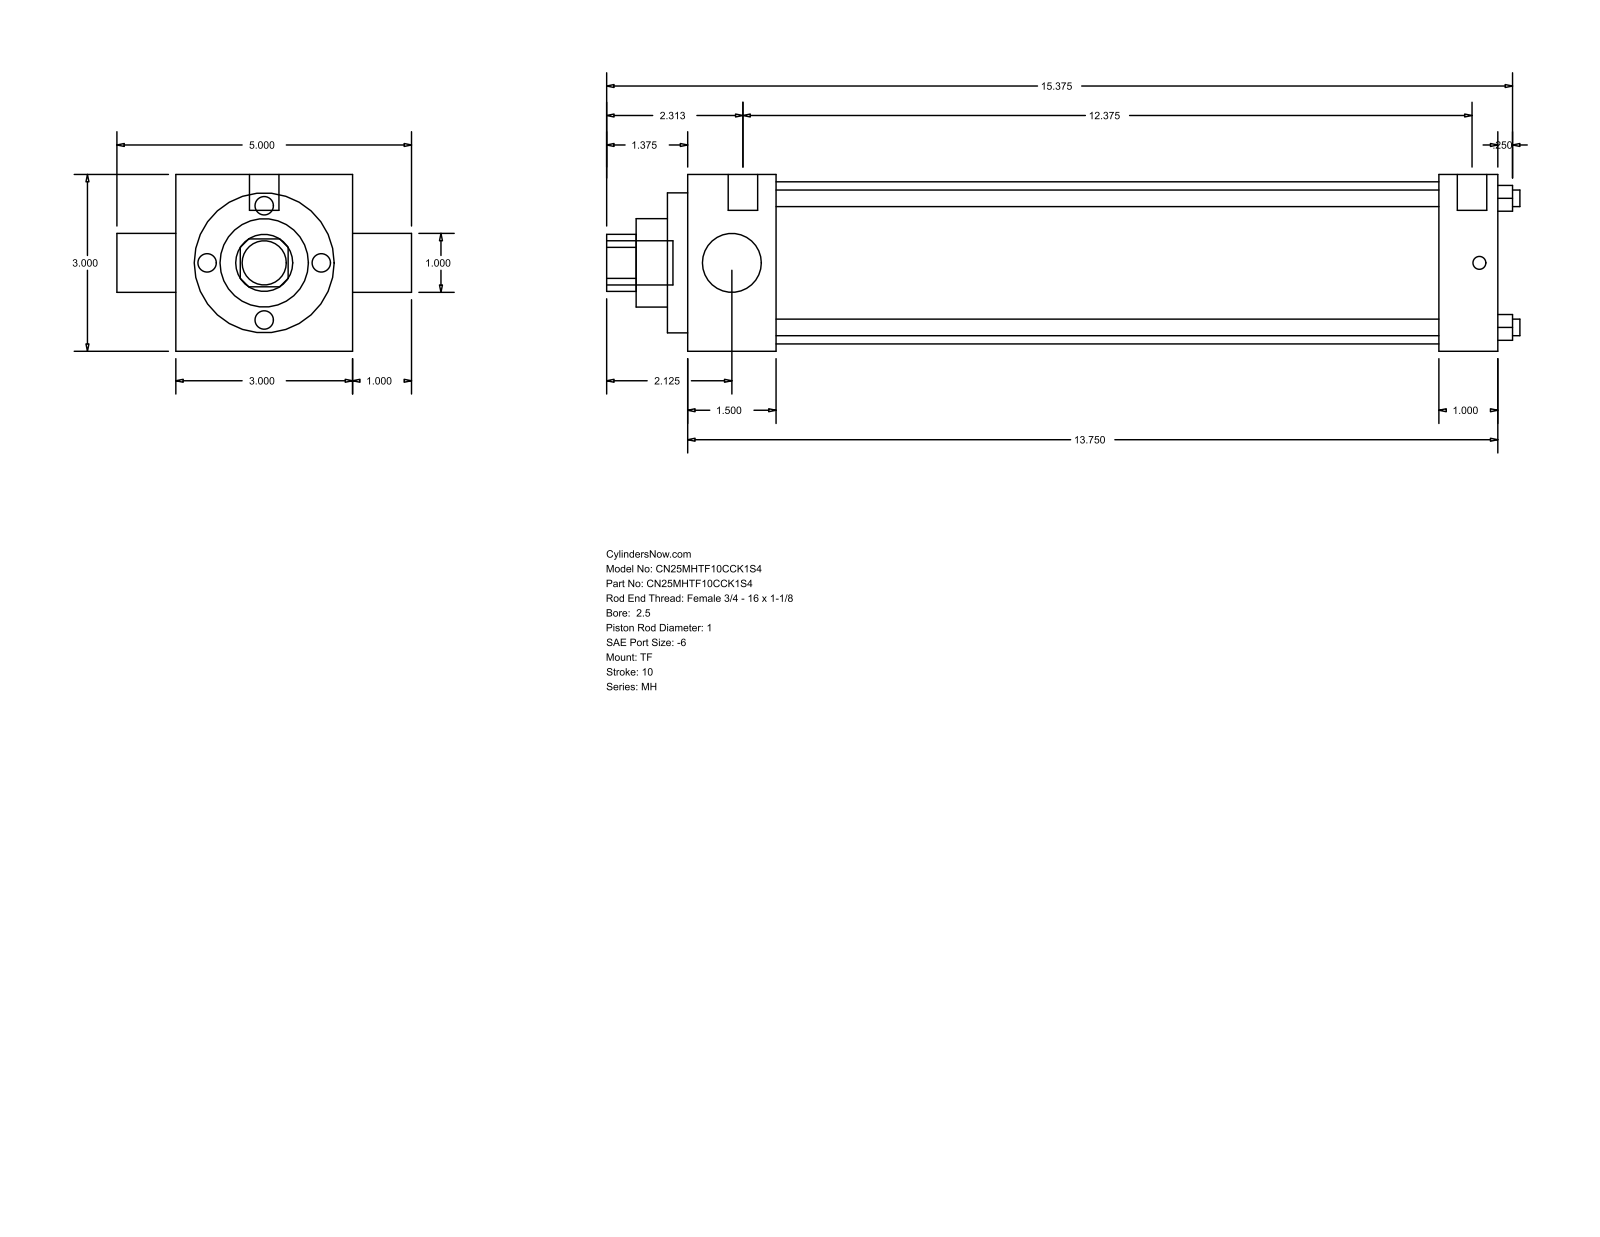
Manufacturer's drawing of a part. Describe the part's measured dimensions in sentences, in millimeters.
The part is named "MH_TF__0250_1". Its 3-D file was written by "GSSL Pune (CONFIG_CONTROL_DESIGN)". It is 0 solids with 86 faces: 61 planar, 25 cylindrical and 0 other. Overall it measures 393.7 by 127 by 76.2 millimeters. Round holes: 4 of diameter 7.14, 2 of diameter 25.4, 1 of diameter 38.1, 1 of diameter 60.33, 1 of diameter 69.85. Round bosses or shafts: 3 of diameter 5.56, 2 of diameter 12.7, 1 of diameter 19.05. Partial cylindrical surfaces (rounded edges, fillets, slot ends): 1 of radius 12.29. The main face-to-face distances are 76.2, 349.26, 38.11, 311.15, 323.85, 285.74, 25.41, 8.73, 46.84, 332.58. The hole center spacings are 39.33, 55.62, 78.66.
